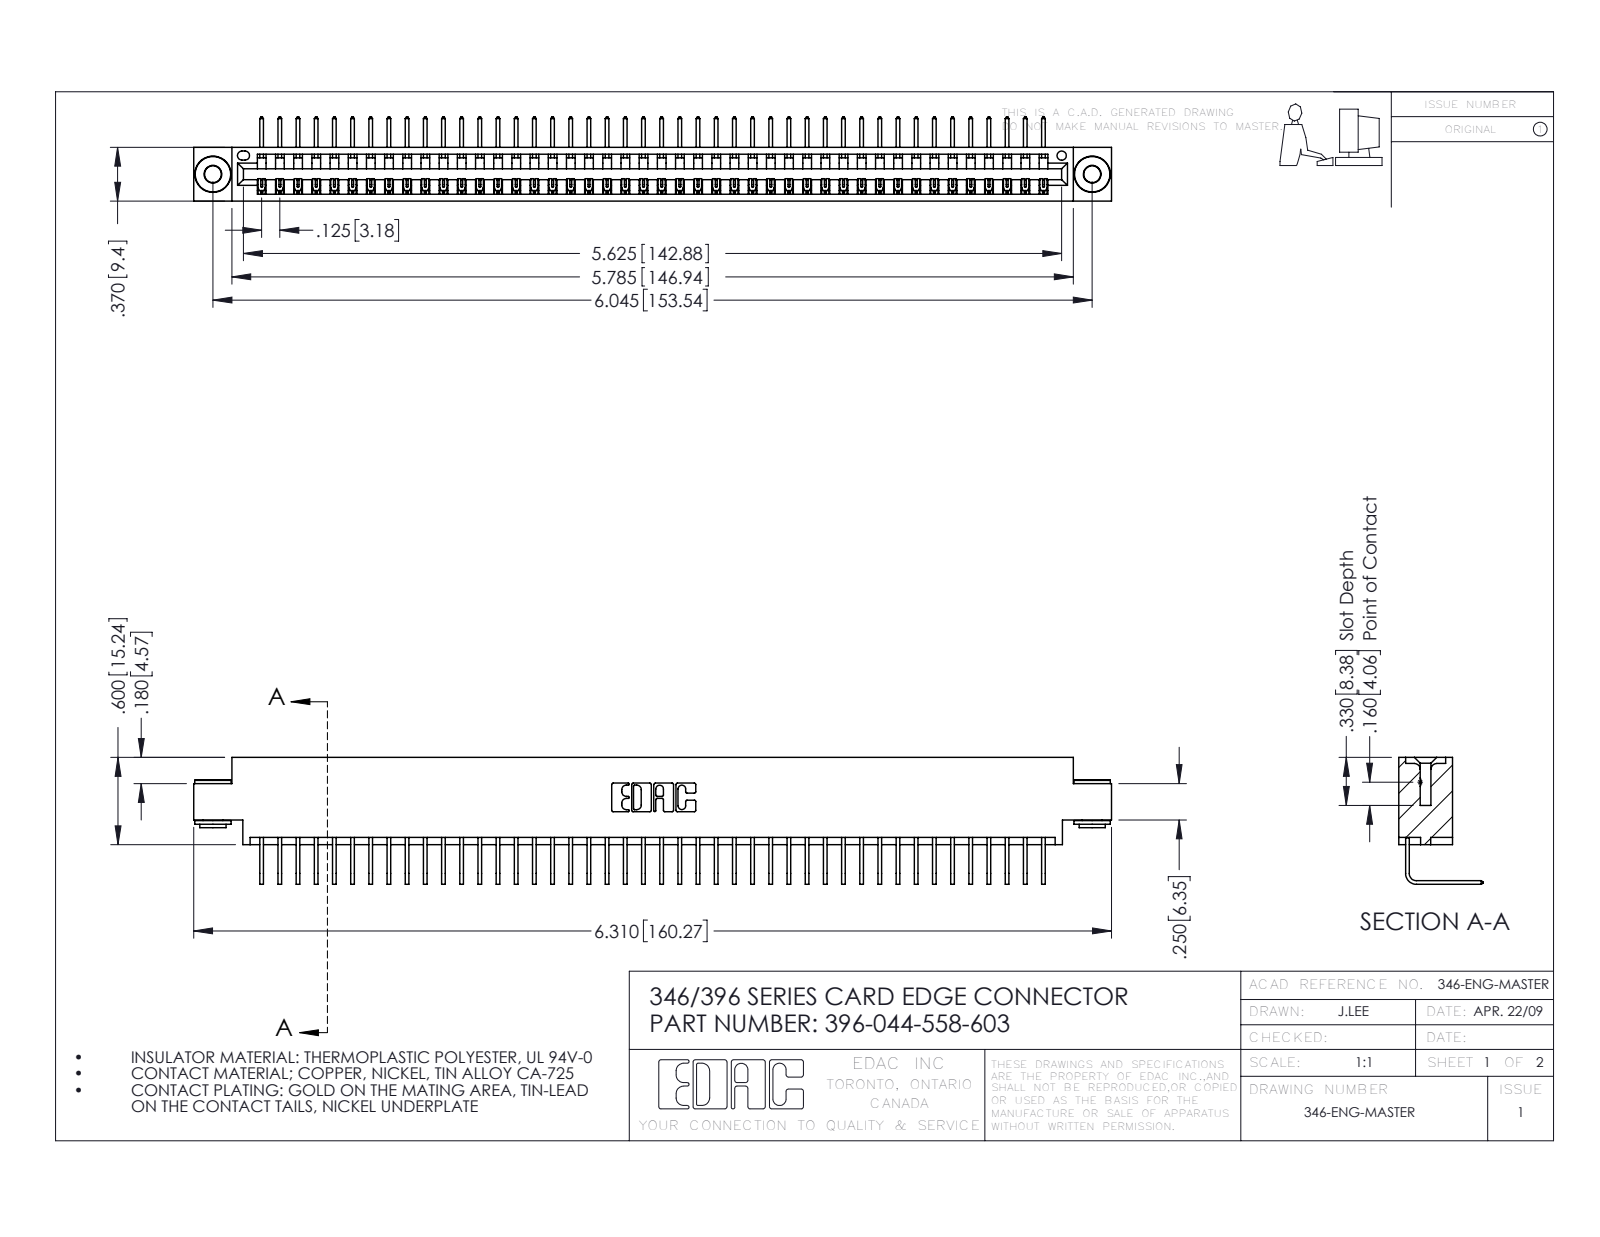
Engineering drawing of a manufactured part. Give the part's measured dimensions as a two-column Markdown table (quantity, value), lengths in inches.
| quantity | value |
| --- | --- |
| part name | 346 Part_0.170 Offset - 0.156 Dia-TH; 345-250-002_345-250-002-102; 396-044-558-603; 345-292-001_558 Tail - 2 |
| STEP written by | SolidWorks 2016 (CONFIG_CONTROL_DESIGN) |
| units | inches |
| bodies | 47 solids, 2804 faces (1938 planar, 858 cylindrical, 8 other) |
| overall size | 6.31 × 0.873 × 0.58 |
| volume | 0.938 in³ |
| surface area | 31.75 in² |
| round holes (diameter × count) | 0.116 × 2, 0.156 × 2, 0.064 × 1 |
| round bosses / shafts (diameter × count) | 0.25 × 2, 0.18 × 2, 0.136 × 2 |
| partial cylindrical surfaces (radius × count) | 0.006 × 88, 0.01 × 22, 0.007 × 6, 0.031 × 6, 0.026 × 3, 0.031 × 2, 0.04 × 2, 0.014 × 1 |
| main face-to-face distances | 0.322, 0.048, 0.37, 0.25, 0.025, 0.298, 0.072, 0.148, 0.222, 0.1 |
| hole center spacings | 0.246, 5.836, 6.045 |
